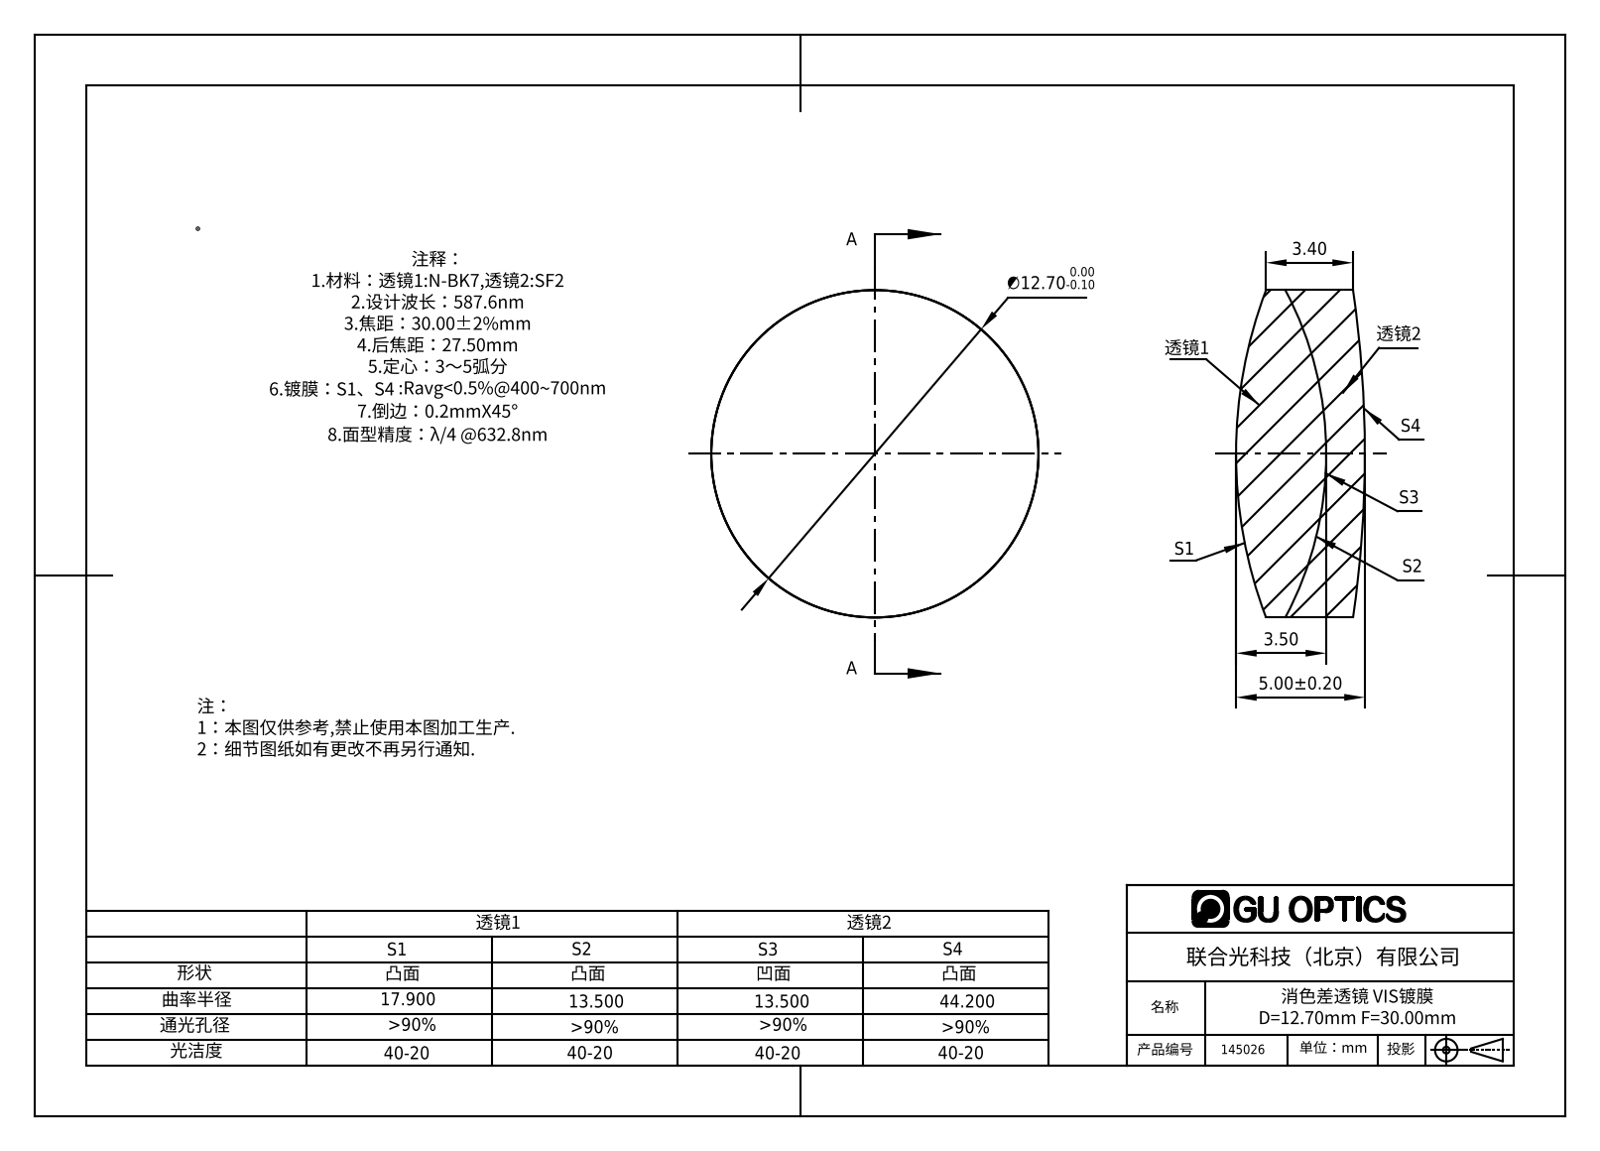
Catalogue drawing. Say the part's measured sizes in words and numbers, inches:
The part is named "145026". Its 3-D file was written by "SolidWorks 2016 (AUTOMOTIVE_DESIGN)". It is 2 solids with 12 faces: 0 planar, 4 cylindrical and 8 other. Overall it measures 0.5 by 0.5 by 0.197 inches. Its volume is 0.032 cubic inches and its surface area 1.03 square inches. Round bosses or shafts: 1 of diameter 0.5.
